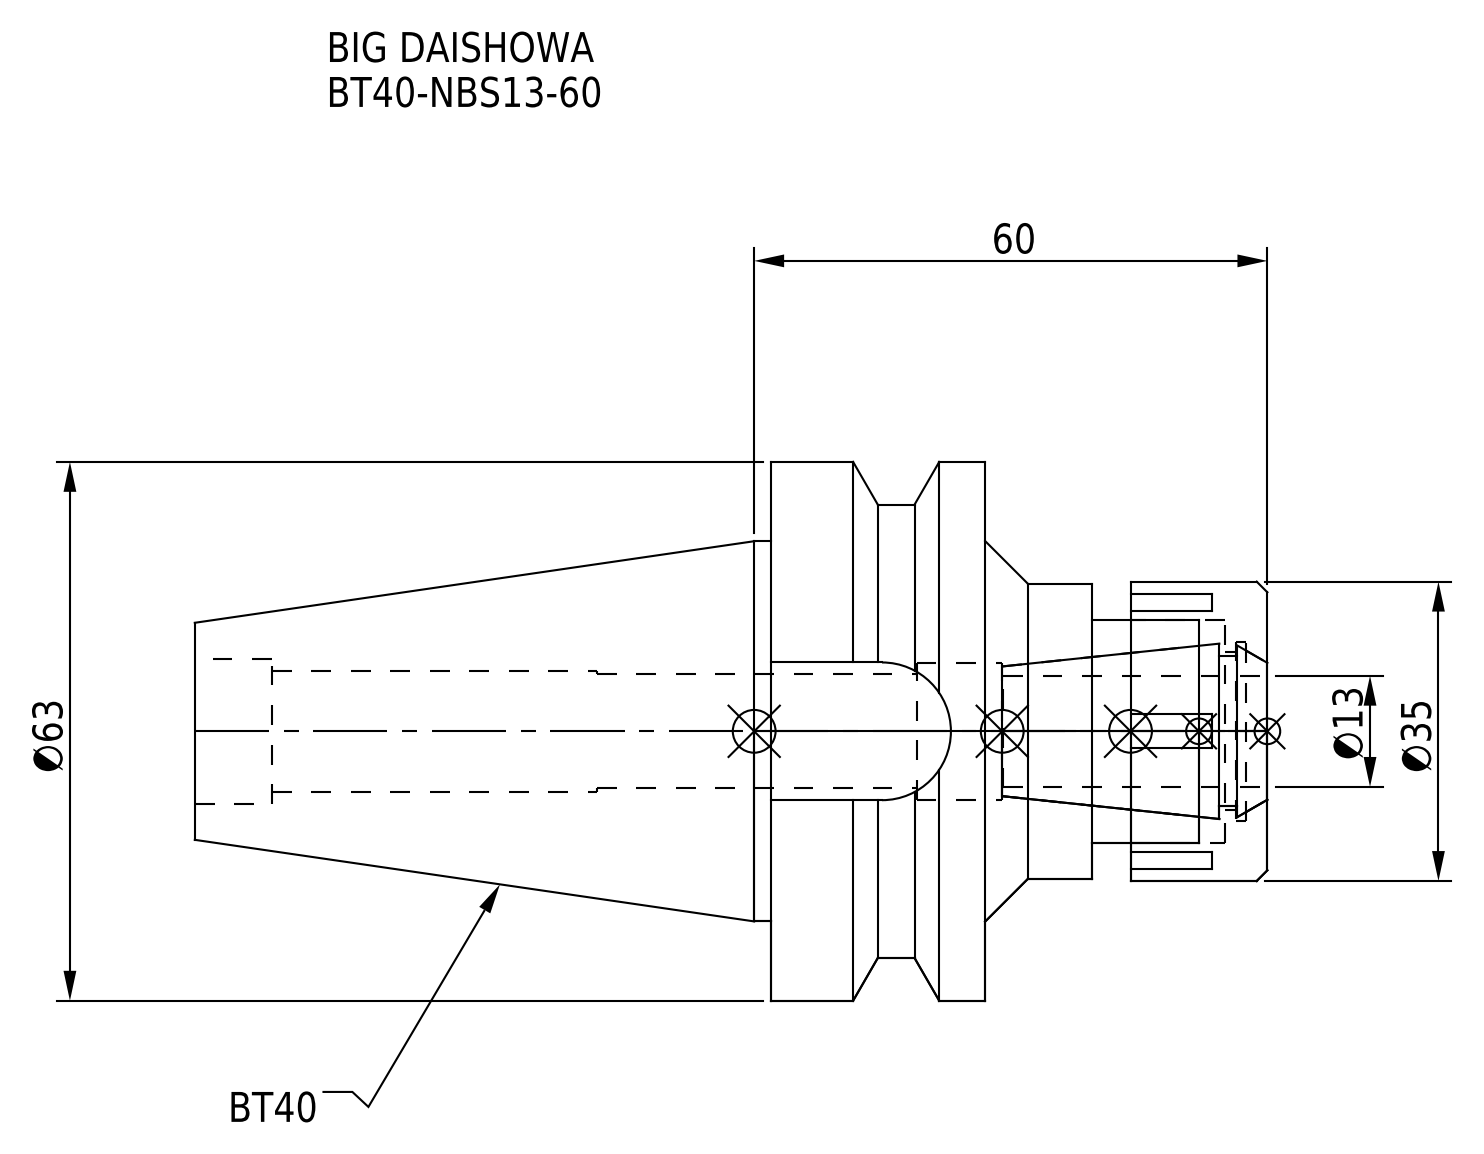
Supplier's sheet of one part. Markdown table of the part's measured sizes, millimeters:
| quantity | value |
| --- | --- |
| part name | BT40-NBS13-60; BT40-NBS13-60-FreeParts; DXF_TEMP_ASSY_ASM_4_ASM.stp; BT40-NBS13-60_1.stp (+3 more) |
| STEP written by | SolidWorks 2019 (CONFIG_CONTROL_DESIGN) |
| units | millimeters |
| bodies | 2 solids, 90 faces (44 planar, 32 cylindrical, 14 other) |
| overall size | 125.4 × 63 × 63 |
| volume | 140 758 mm³ |
| surface area | 30 719 mm² |
| round holes (diameter × count) | 13.3 × 1, 14.2 × 1, 16 × 1, 17 × 1, 18.5 × 1, 21 × 1, 26 × 1 |
| round bosses / shafts (diameter × count) | 63 × 1, 53 × 1, 44.45 × 1, 35 × 1, 34.5 × 1 |
| partial cylindrical surfaces (radius × count) | 8.05 × 1 |
| main face-to-face distances | 25, 33, 58, 12.5, 8, 37.5, 20.5, 17, 16, 4.5 |
